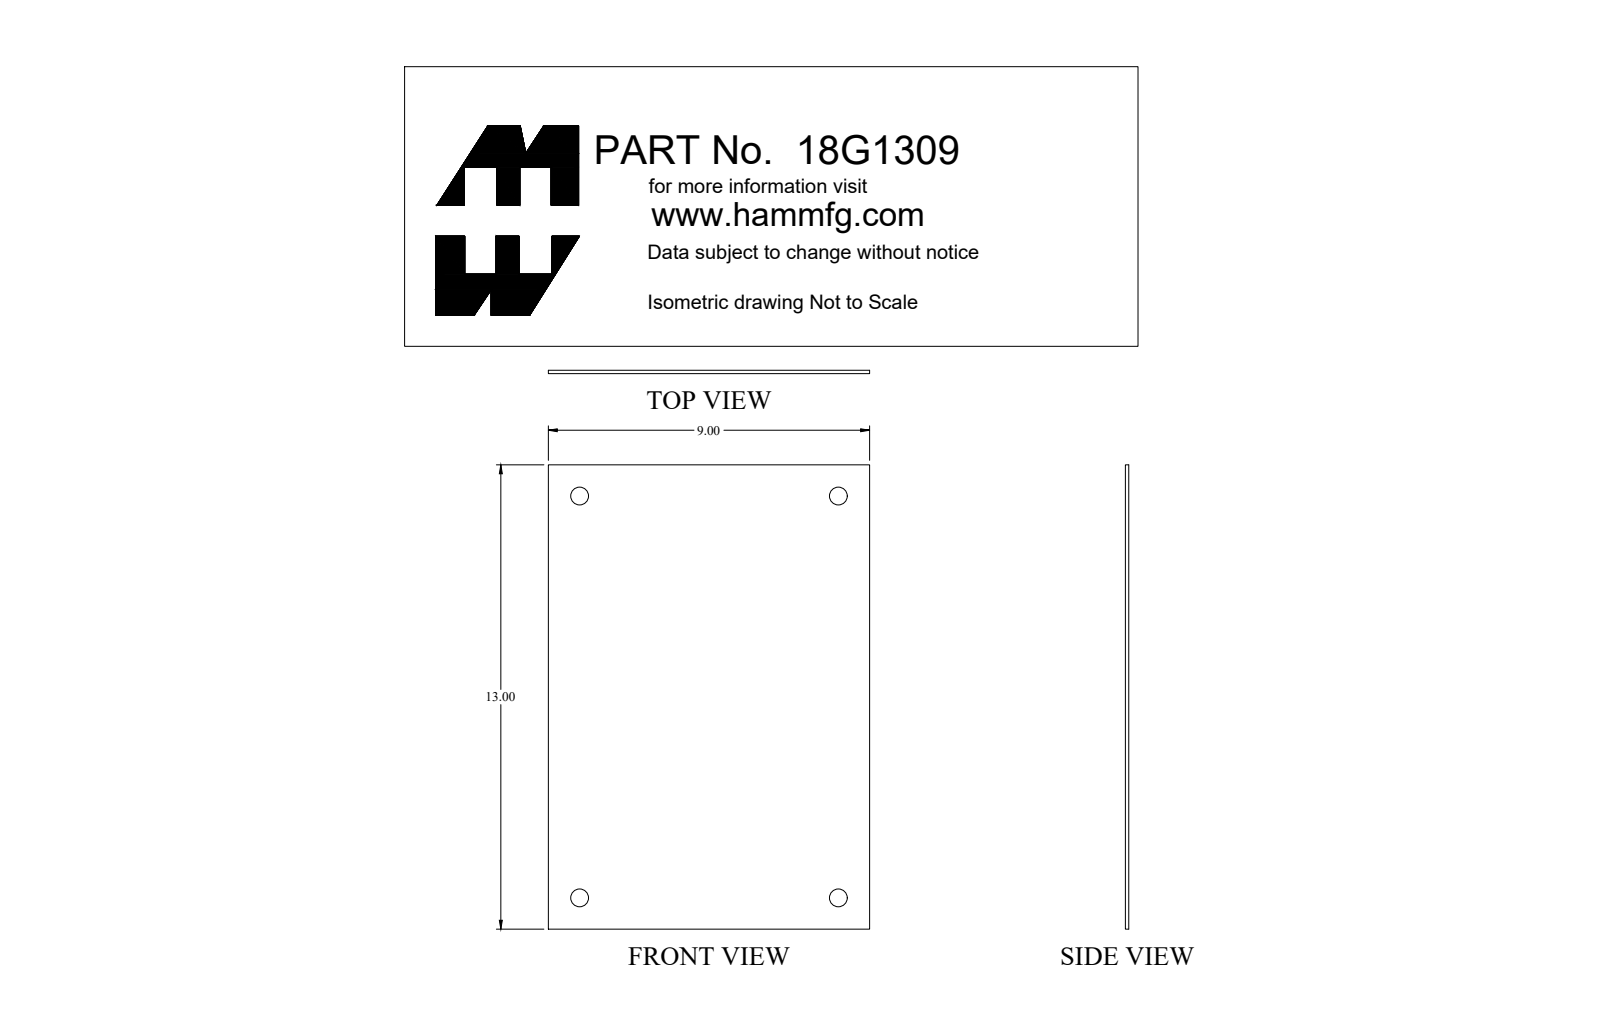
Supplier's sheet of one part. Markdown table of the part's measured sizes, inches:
| quantity | value |
| --- | --- |
| part name | 18G1309 |
| STEP written by | SolidWorks 2018 (AUTOMOTIVE_DESIGN) |
| units | inches |
| bodies | 1 solid, 10 faces (6 planar, 4 cylindrical, 0 other) |
| overall size | 13 × 9 × 0.095 |
| volume | 11.04 in³ |
| surface area | 237.2 in² |
| round holes (diameter × count) | 0.5 × 4 |
| main face-to-face distances | 0.095, 9, 13 |
| hole center spacings | 7.25, 11.25, 13.384 |
